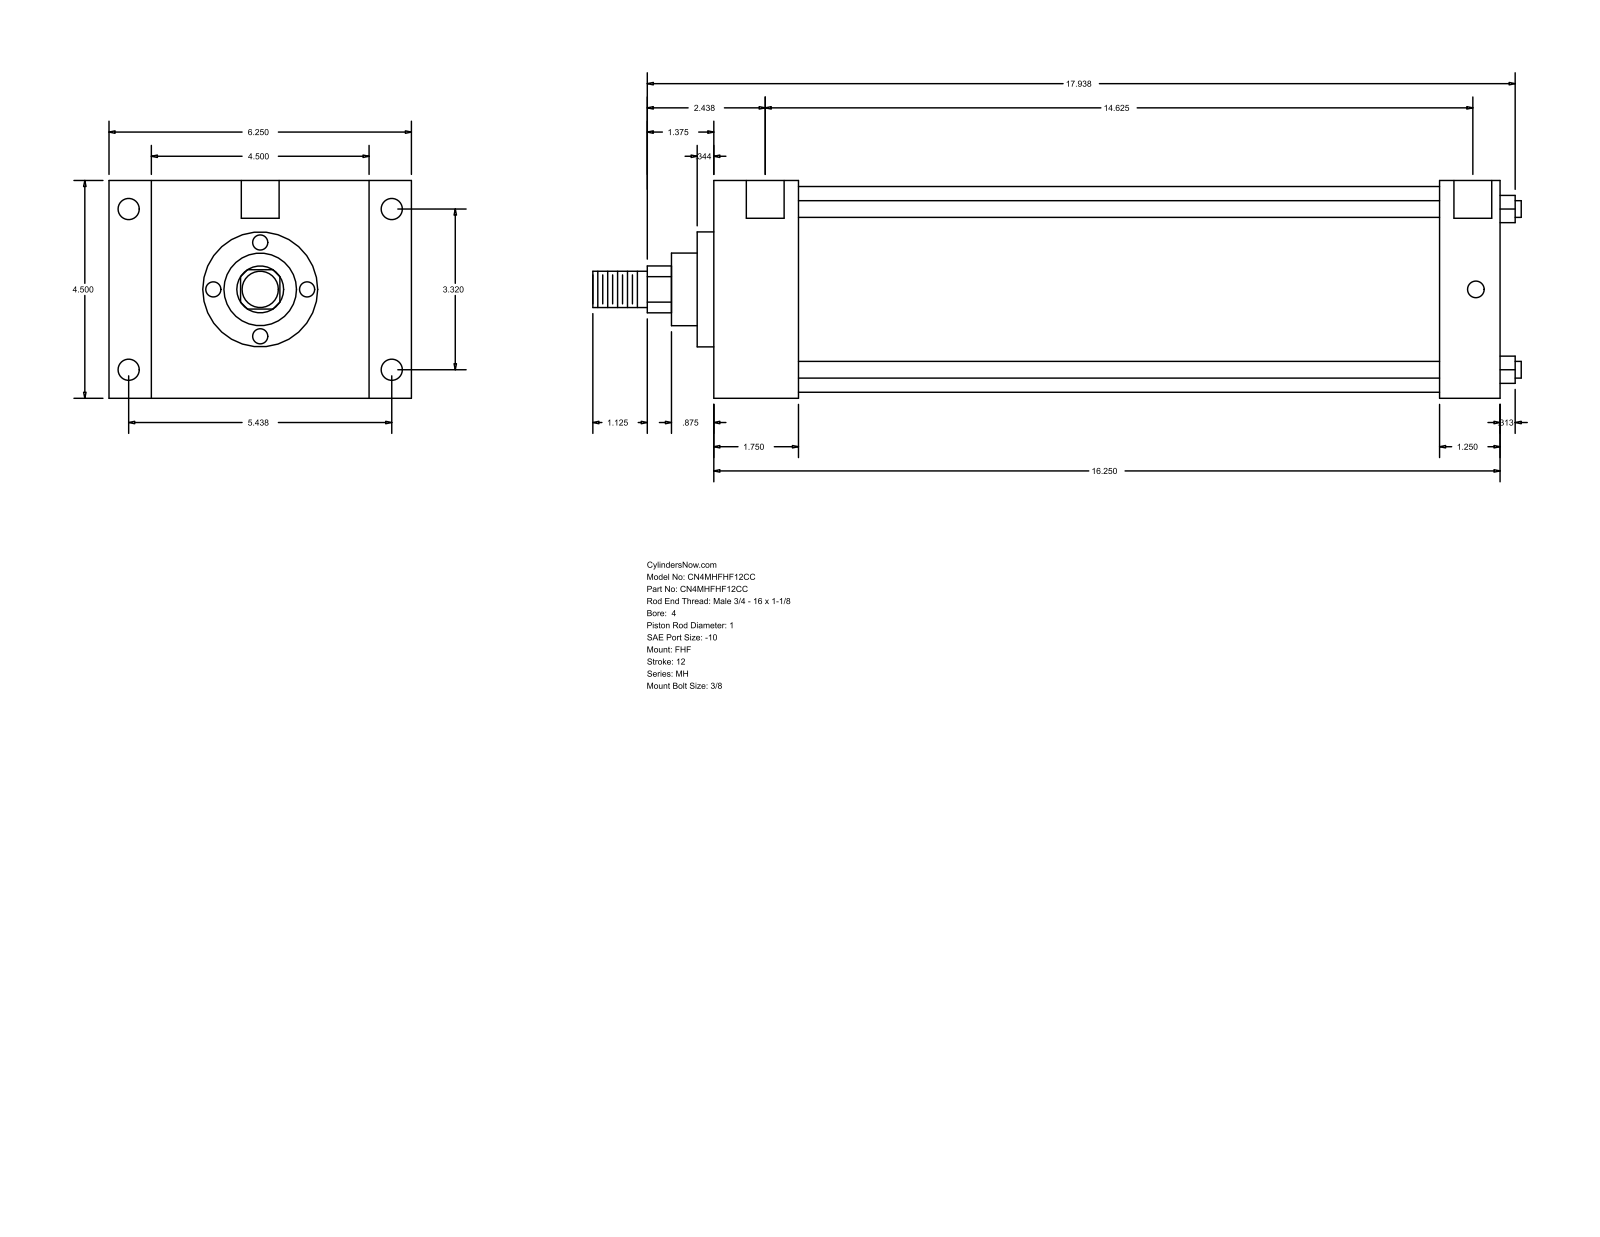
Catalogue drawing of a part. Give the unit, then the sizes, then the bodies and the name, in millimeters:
Units: millimetres
Overall size (bounding box): 487.36 × 158.75 × 114.3
Round holes (diameter × count): ⌀8.73 ×4, ⌀11.13 ×4, ⌀19.84 ×2
Round bosses / shafts (diameter × count): ⌀8.76 ×4, ⌀107.95 ×1, ⌀60.33 ×1, ⌀38.1 ×1, ⌀25.4 ×1, ⌀19.05 ×1
Partial cylindrical surfaces — rounded edges, fillets, slot ends (radius × count): R12.29 ×1
Main face-to-face distances: 114.3, 412.76, 44.46, 368.3, 22.23, 136.53, 158.76, 381.01, 336.55, 31.75
Hole centre spacings: 84.32, 138.12, 161.82, 374.65, 1.58, 1.59, 371.48, 373.06
Bodies: 0 solids, 90 faces (61 planar, 29 cylindrical, 0 other)
Part name (STEP PRODUCT): MH_FHF__0400_1
STEP written by: GSSL Pune (CONFIG_CONTROL_DESIGN)
